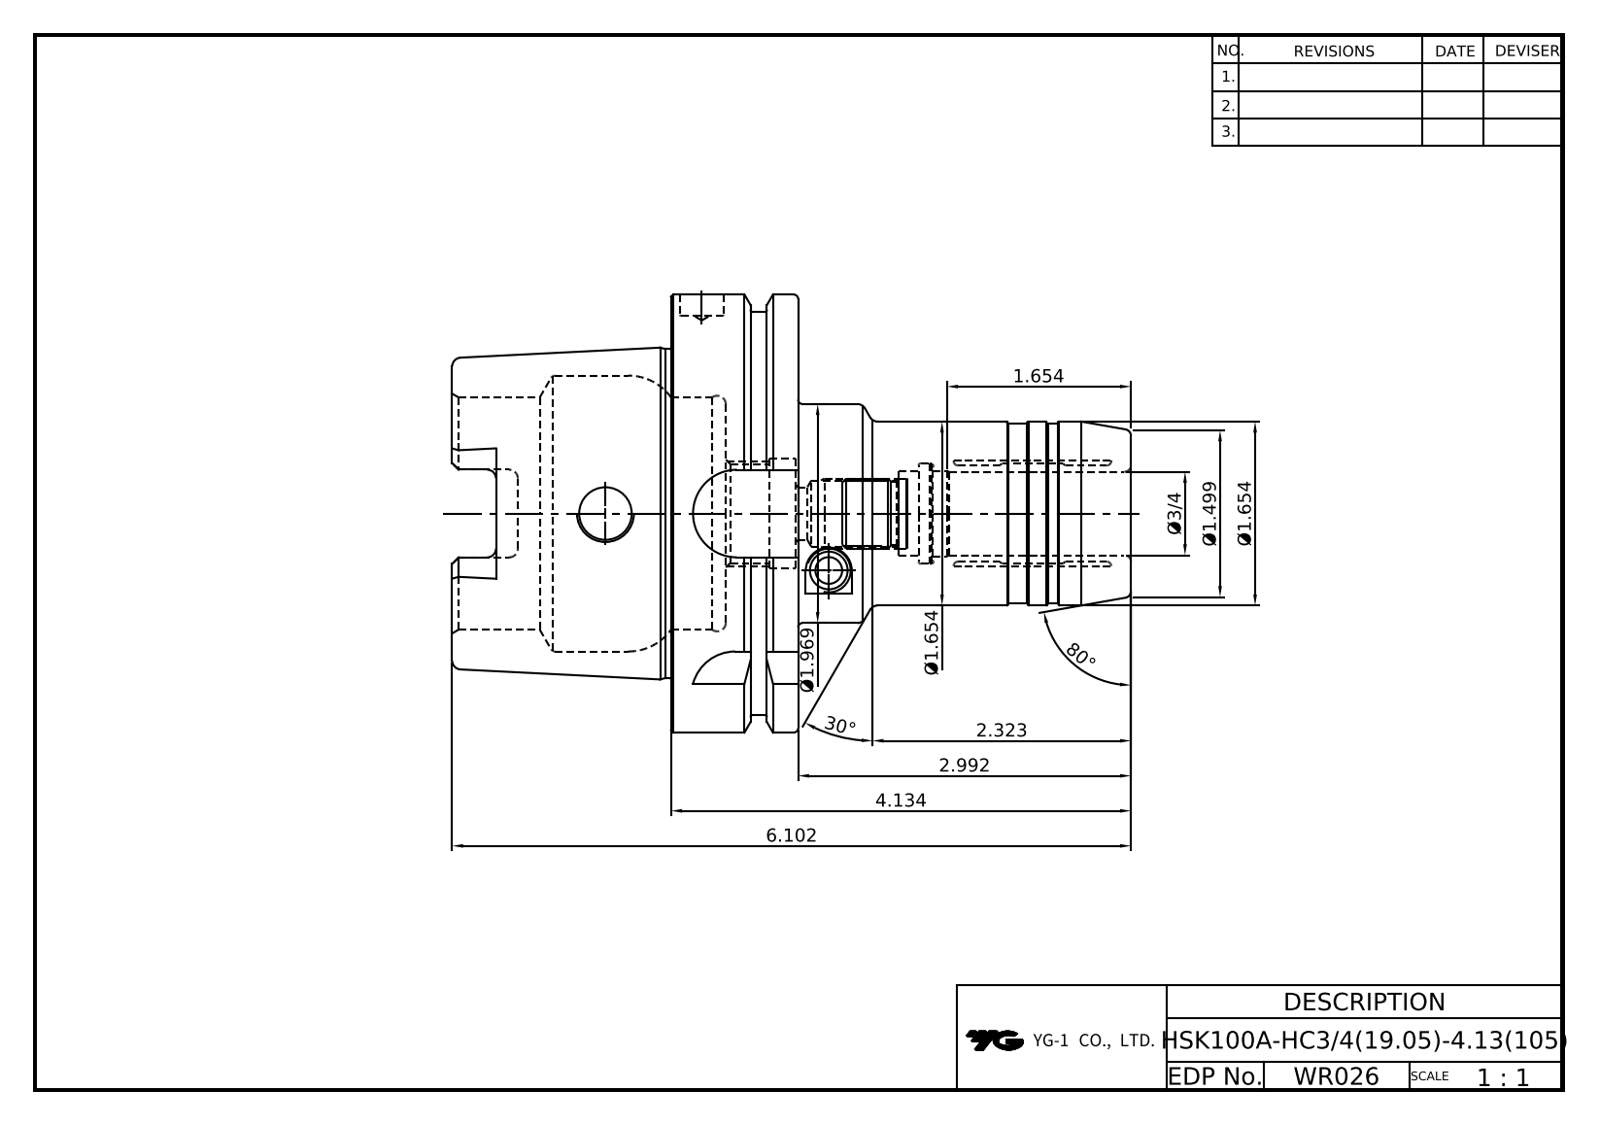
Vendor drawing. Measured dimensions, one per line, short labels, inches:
name: HSK100A-HC19.05-105
written by: Autodesk Inventor 2020 (AUTOMOTIVE_DESIGN)
unit: in
bodies: 1 solid, 136 faces (38 planar, 40 cylindrical, 58 other)
size: 6.102 × 3.937 × 3.937
volume: 21.21 in³; area: 98.39 in²
holes: 2× ⌀0.472, 1× ⌀0.394, 1× ⌀0.587, 1× ⌀0.75, 1× ⌀0.764, 1× ⌀0.881, 1× ⌀0.984, 1× ⌀2.087, 1× ⌀2.48
bosses: 1× ⌀3.937, 1× ⌀3.622, 1× ⌀2.969, 1× ⌀1.969, 1× ⌀1.654, 1× ⌀1.614
rounds: 6× R0.079, 4× R0.192, 4× R0.394
face distances: 1.142, 0.492, 0.65, 2.461, 1.969, 3.11, 6.102, 4.134, 3.642, 2.992
